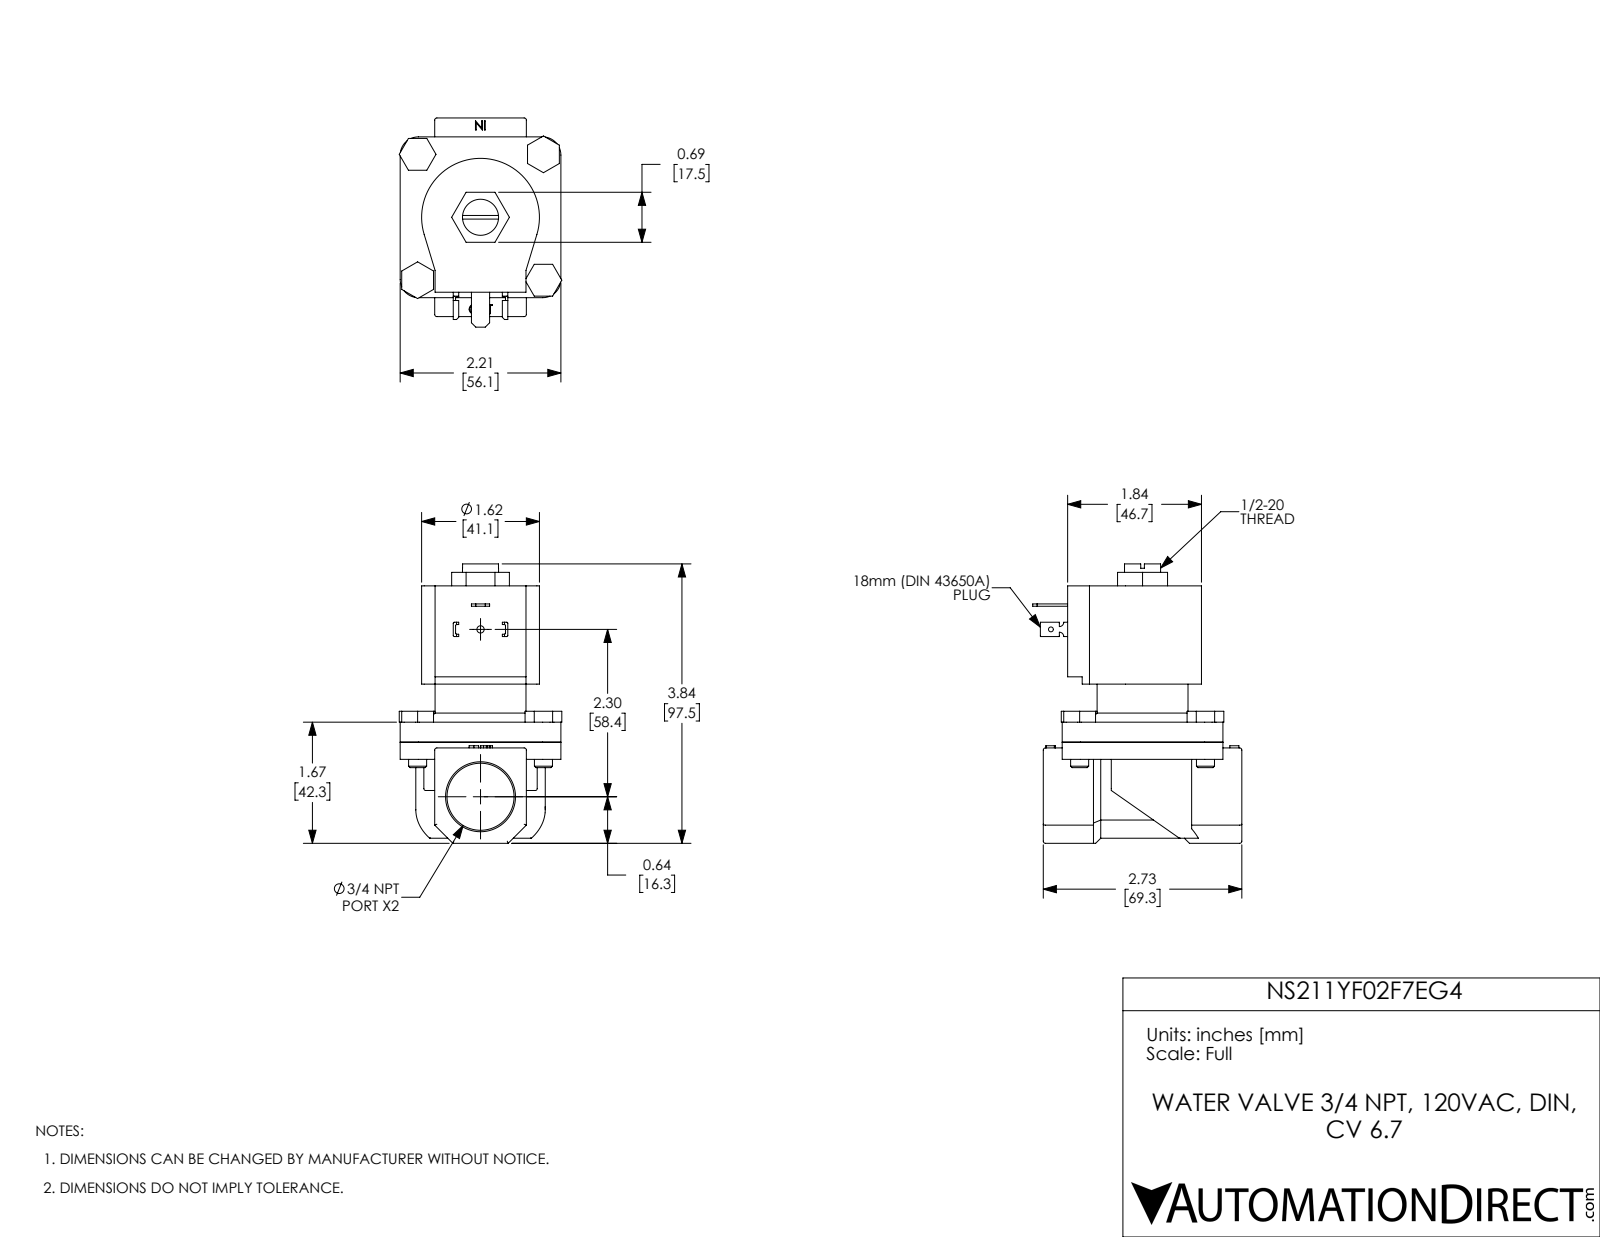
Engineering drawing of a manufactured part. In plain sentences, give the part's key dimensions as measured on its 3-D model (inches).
The part is named "NS211YF02F7EG5". Its 3-D file was written by "SolidWorks 2017 (AUTOMOTIVE_DESIGN)". It is 11 solids with 332 faces: 198 planar, 99 cylindrical and 35 other. Overall it measures 3.84 by 2.875 by 2.235 inches. Its volume is 9.853 cubic inches and its surface area 64.15 square inches. Round holes: 4 of diameter 0.25, 1 of diameter 0.067, 1 of diameter 0.1, 1 of diameter 0.496, 1 of diameter 0.512, 1 of diameter 0.922, 1 of diameter 1.155. Round bosses or shafts: 4 of diameter 0.248, 1 of diameter 1.25. Partial cylindrical surfaces (rounded edges, fillets, slot ends): 15 of radius 0.03, 8 of radius 0.015, 4 of radius 0.25, 2 of radius 0.06, 1 of radius 0.81, 1 of radius 0.89. The main face-to-face distances are 0.275, 2.148, 1.873, 0.475, 1.735, 2.21, 0.798, 0.523, 1.35, 0.236. The hole center spacings are 1.223, 1.73, 2.446, 2.3.
